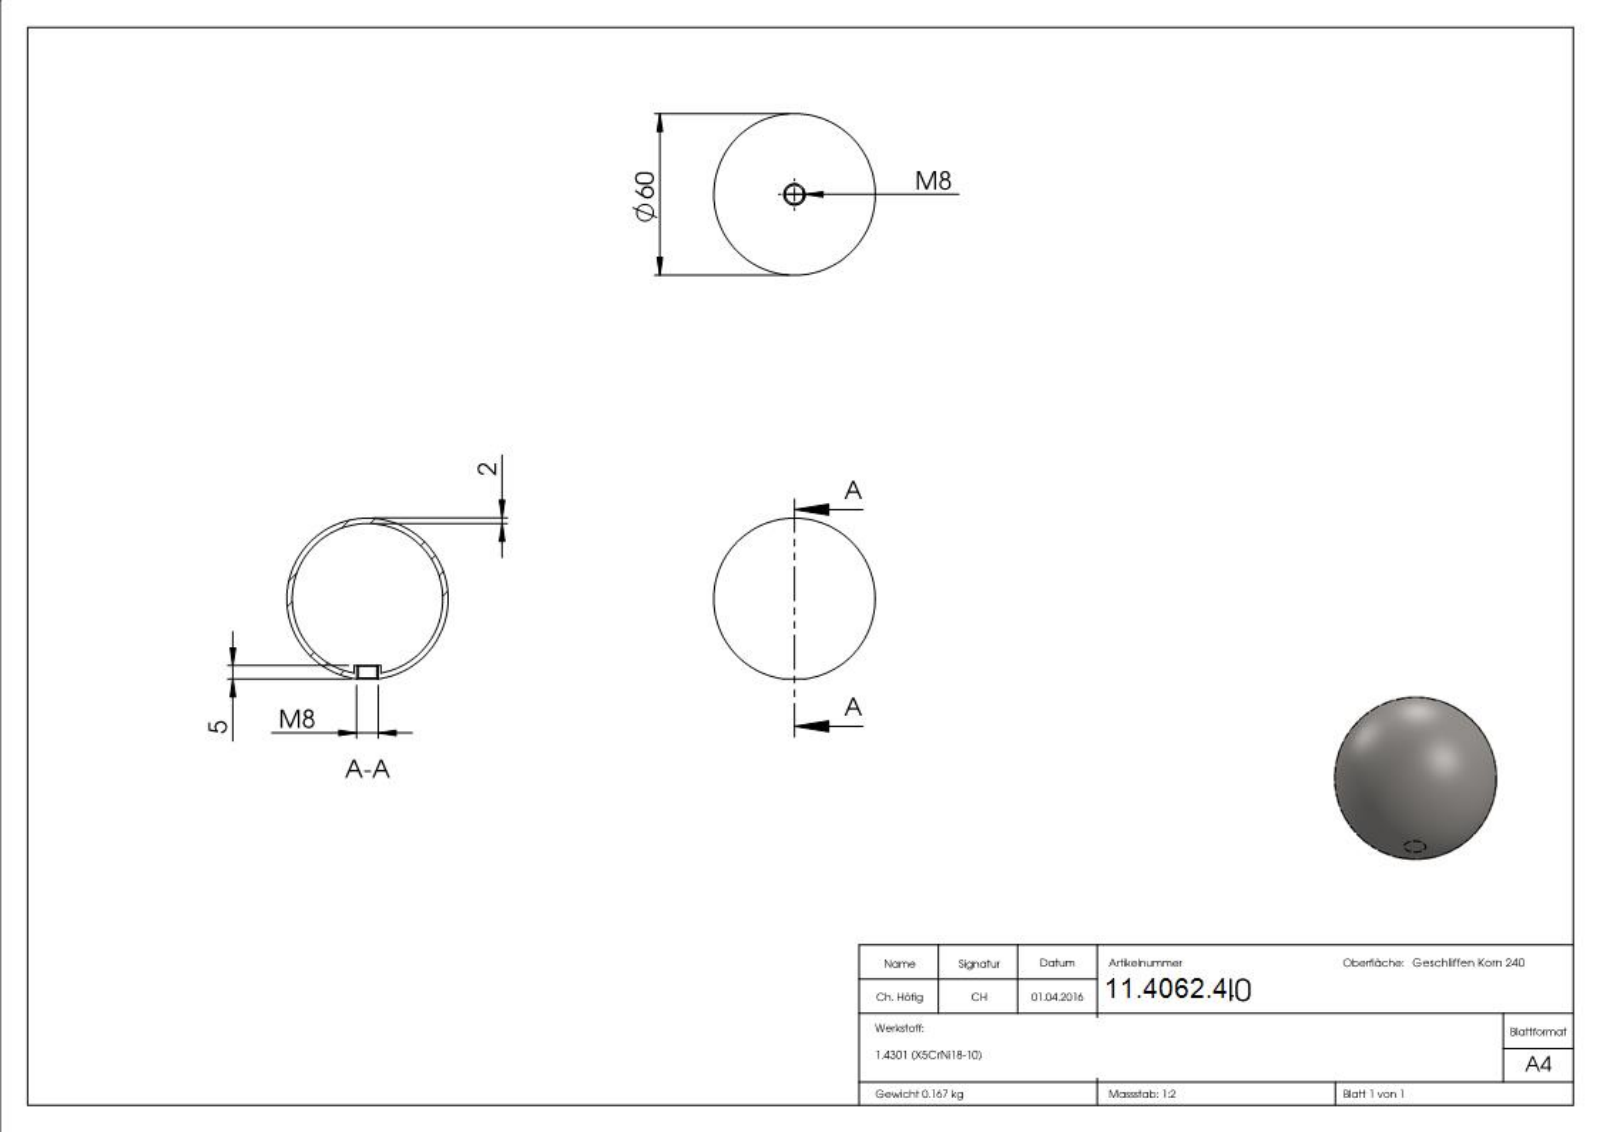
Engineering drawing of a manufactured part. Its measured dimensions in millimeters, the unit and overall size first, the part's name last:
Units: millimetres
Overall size (bounding box): 60 × 60 × 59.75
Round holes (diameter × count): ⌀6.8 ×1
Round bosses / shafts (diameter × count): ⌀10 ×1
Volume: 21 193 mm³ · Surface area: 21 280 mm²
Bodies: 1 solid, 232 faces (93 planar, 4 cylindrical, 135 other)
Part name (STEP PRODUCT): 52060-240
STEP written by: SolidWorks 2015 (CONFIG_CONTROL_DESIGN)
